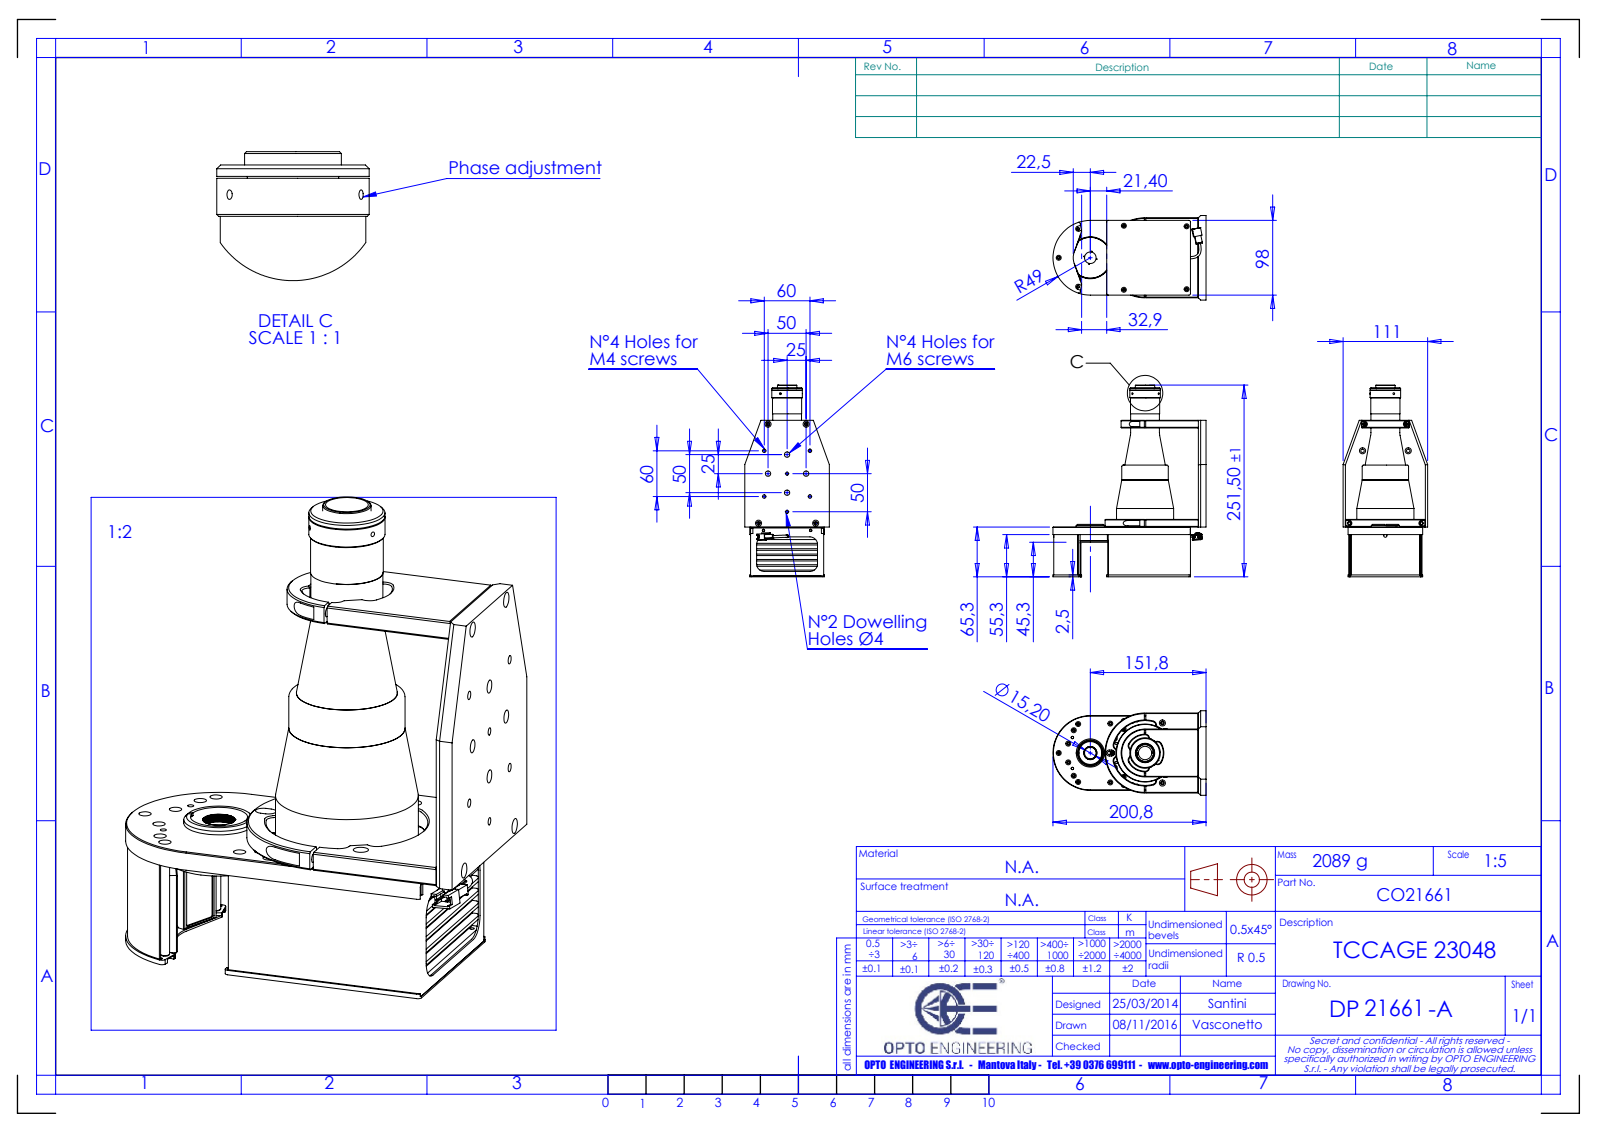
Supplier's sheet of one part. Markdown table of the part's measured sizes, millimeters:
| quantity | value |
| --- | --- |
| part name | DP21661-A |
| STEP written by | SolidWorks 2016 (AUTOMOTIVE_DESIGN) |
| units | millimeters |
| bodies | 0 solids, 745 faces (332 planar, 325 cylindrical, 88 other) |
| overall size | 251.5 × 200.8 × 111 |
| round holes (diameter × count) | 6.5 × 19, 3.5 × 15, 2.5 × 12, 8 × 10, 4.5 × 8, 3.2 × 6, 7 × 4, 1.6 × 2, 3 × 2, 4 × 2, 15.2 × 1, 17 × 1 |
| round bosses / shafts (diameter × count) | 5 × 2, 75 × 1, 61 × 1, 53.5 × 1, 40 × 1, 38.2 × 1, 37.8 × 1, 37 × 1 |
| partial cylindrical surfaces (radius × count) | 1 × 10, 2 × 10, 5 × 8, 3.5 × 4, 4 × 4, 10 × 4, 0.5 × 2, 3 × 2 |
| main face-to-face distances | 10, 1, 65.29, 95, 96, 55.29, 140, 130, 94, 2 |
| hole center spacings | 30.41, 62.65, 25, 35.36, 50, 9.99, 19.01, 31.08 |
